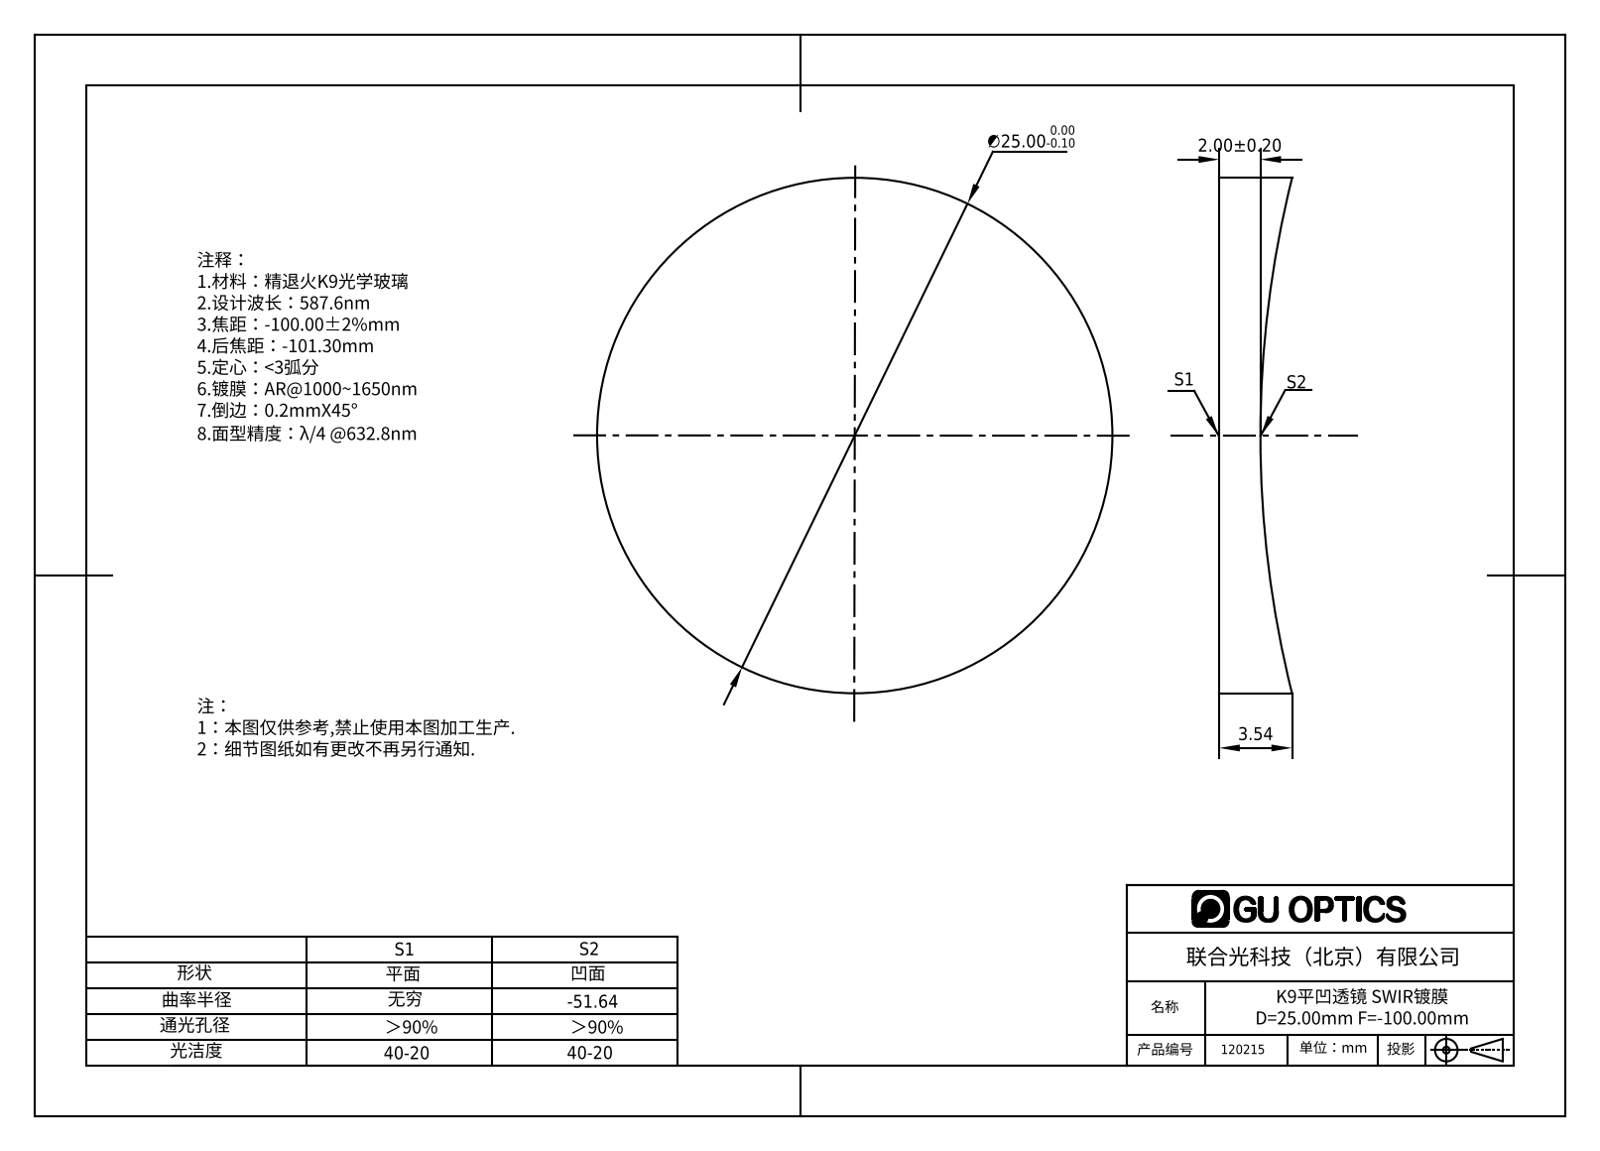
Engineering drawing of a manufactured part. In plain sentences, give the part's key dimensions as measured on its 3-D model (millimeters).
The part is named "120155". Its 3-D file was written by "SolidWorks 2016 (AUTOMOTIVE_DESIGN)". It is 1 solid with 5 faces: 1 planar, 2 cylindrical and 2 other. Overall it measures 25 by 25 by 3.54 millimeters. Its volume is 1 357 cubic millimeters and its surface area 1 267 square millimeters. Round bosses or shafts: 1 of diameter 25.
